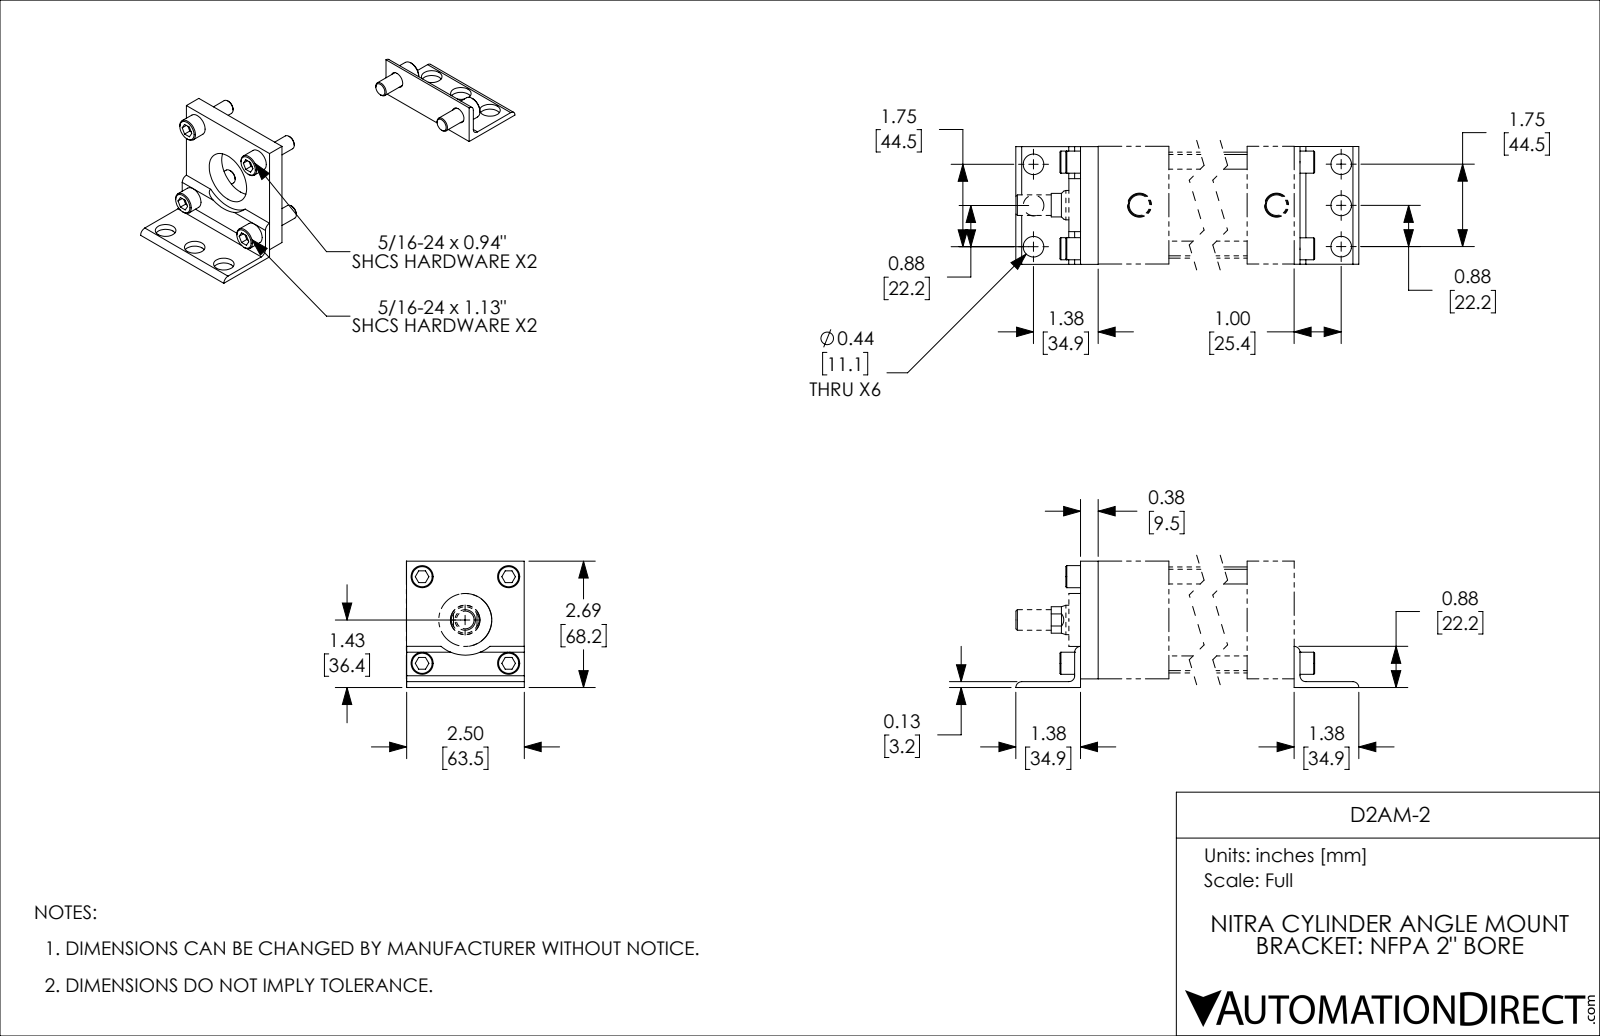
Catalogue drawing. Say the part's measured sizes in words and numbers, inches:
The part is named "D2AM-2_1; D232020DT-M_BODY; D232020DT-M_2; D2AM-2 (+2 more)". Its 3-D file was written by "SolidWorks 2019 (CONFIG_CONTROL_DESIGN)". It is 11 solids with 364 faces: 136 planar, 124 cylindrical and 104 other. Overall it measures 8.75 by 2.685 by 2.507 inches. Its volume is 27 cubic inches and its surface area 189.1 square inches. Round holes: 7 of diameter 0.272, 6 of diameter 0.437, 5 of diameter 0.344, 4 of diameter 0.257, 4 of diameter 0.5, 2 of diameter 0.438, 1 of diameter 0.626, 1 of diameter 1.125, 1 of diameter 1.875, 1 of diameter 2.001. Round bosses or shafts: 9 of diameter 0.312, 5 of diameter 0.469, 1 of diameter 2.251, 1 of diameter 1.999, 1 of diameter 1.125, 1 of diameter 0.624, 1 of diameter 0.437. Partial cylindrical surfaces (rounded edges, fillets, slot ends): 6 of radius 0.125, 1 of radius 0.281, 1 of radius 0.813. The main face-to-face distances are 2.5, 4.625, 1, 0.185, 5.625, 2.685, 4.125, 0.125, 5, 6. The hole center spacings are 1.838, 1.844, 1.84, 1.301, 1.304, 0.875, 0.875, 1.3.
